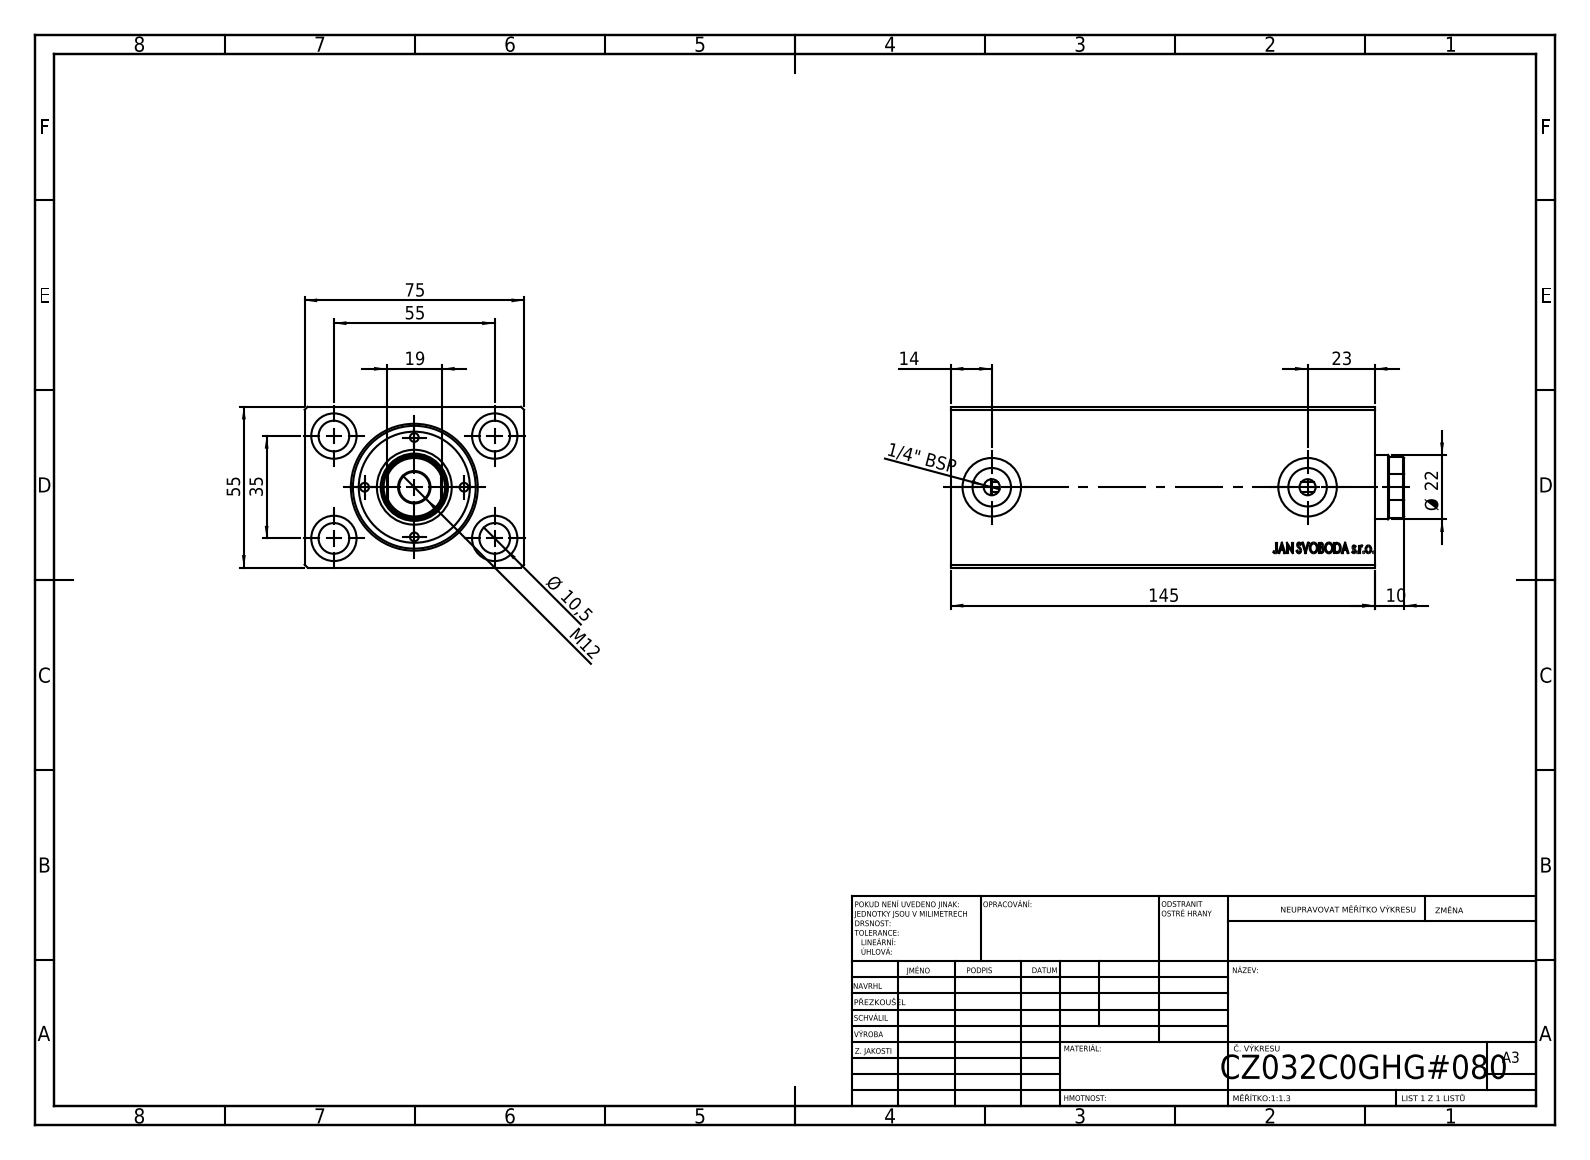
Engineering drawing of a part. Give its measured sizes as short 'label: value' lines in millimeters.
written by: SolidWorks 2019 (CONFIG_CONTROL_DESIGN)
unit: mm
bodies: 1 solid, 826 faces (398 planar, 46 cylindrical, 382 other)
size: 145 × 75 × 55
volume: 423 431 mm³; area: 80 331 mm²
holes: 4× ⌀10.5, 4× ⌀15.5, 2× ⌀5.5, 2× ⌀8, 2× ⌀13.16, 2× ⌀20, 1× ⌀32, 1× ⌀36, 1× ⌀42
face distances: 55, 75, 145, 13.6, 144.8, 10.33, 134.67, 131.2, 13.8, 10
hole spacings: 32.6, 35, 55, 65.19, 88, 108
